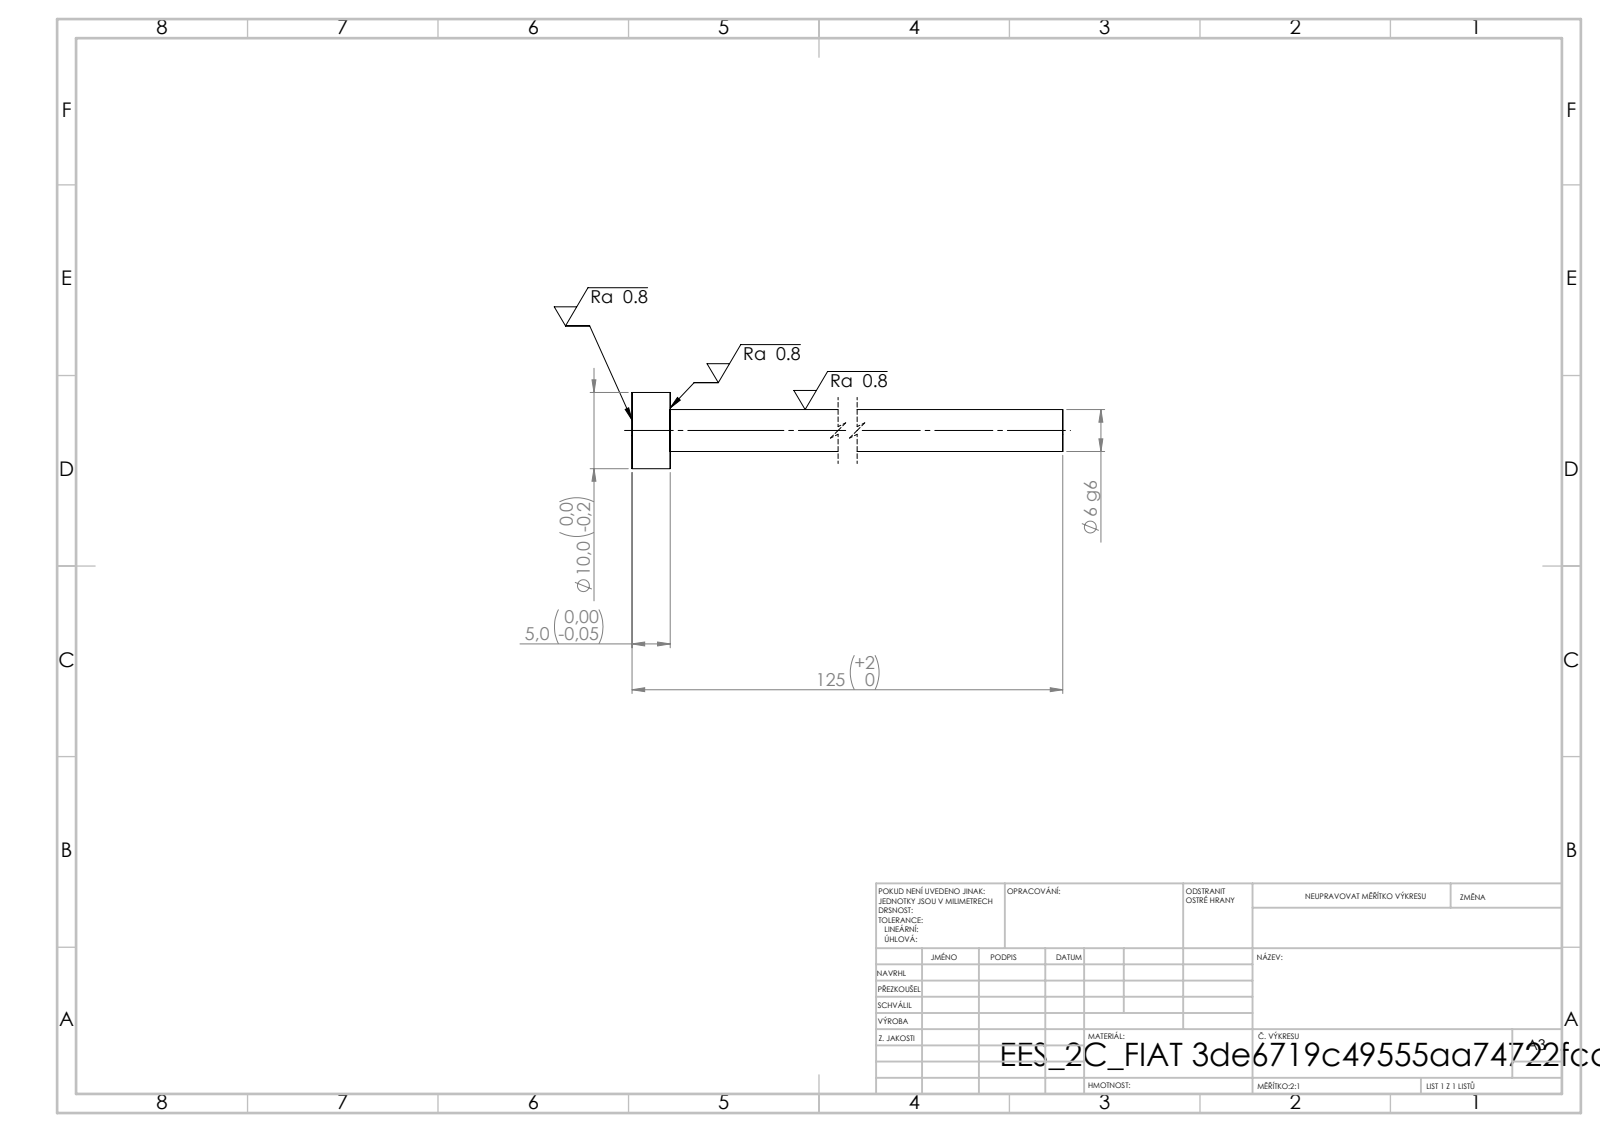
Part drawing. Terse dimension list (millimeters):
written by: SolidWorks 2019 (CONFIG_CONTROL_DESIGN)
unit: mm
bodies: 1 solid, 7 faces (3 planar, 4 cylindrical, 0 other)
size: 125 × 10 × 10
volume: 3 244 mm³; area: 2 388 mm²
bosses: 1× ⌀10, 1× ⌀5.5
face distances: 5, 125, 120
